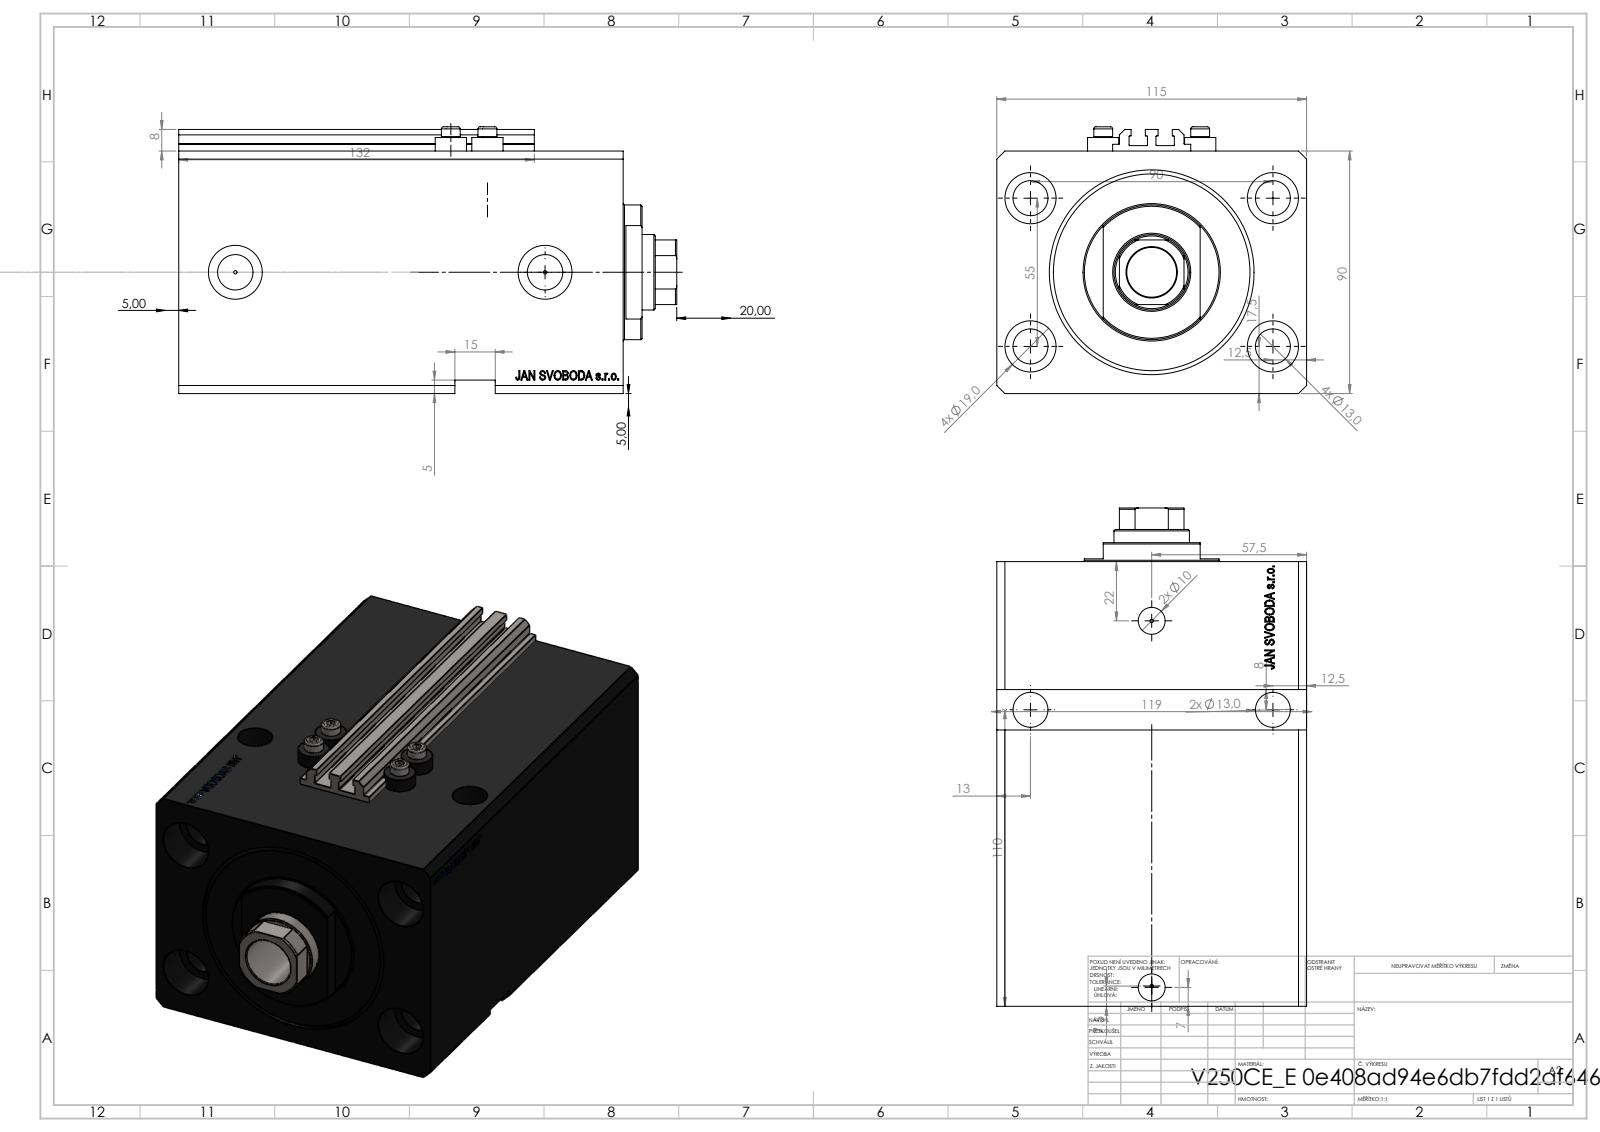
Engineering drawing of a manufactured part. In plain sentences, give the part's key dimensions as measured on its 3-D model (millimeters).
The part is named "V250CE_VC_E; ALLEN BOLT V250CE; V250CE_E_Body; V250CE_C_VCP". Its 3-D file was written by "SolidWorks 2019 (CONFIG_CONTROL_DESIGN)". It is 8 solids with 1115 faces: 543 planar, 134 cylindrical and 438 other. Overall it measures 185 by 115 by 99 millimeters. Its volume is 1 394 000 cubic millimeters and its surface area 213 348 square millimeters. Round holes: 6 of diameter 13, 4 of diameter 1.25, 4 of diameter 4, 4 of diameter 19, 2 of diameter 8.5, 2 of diameter 10, 2 of diameter 13.16, 2 of diameter 20, 1 of diameter 18.5, 1 of diameter 28, 1 of diameter 63, 1 of diameter 76. Round bosses or shafts: 4 of diameter 11.6, 4 of diameter 7, 1 of diameter 50. Partial cylindrical surfaces (rounded edges, fillets, slot ends): 10 of radius 0.2, 1 of radius 13.5. The main face-to-face distances are 90, 115, 165, 20, 17.9, 147.1, 145, 127.1, 65, 80. The hole center spacings are 52.74, 90, 13.6, 14.76, 27.39, 27.51, 28.46, 29.73.
